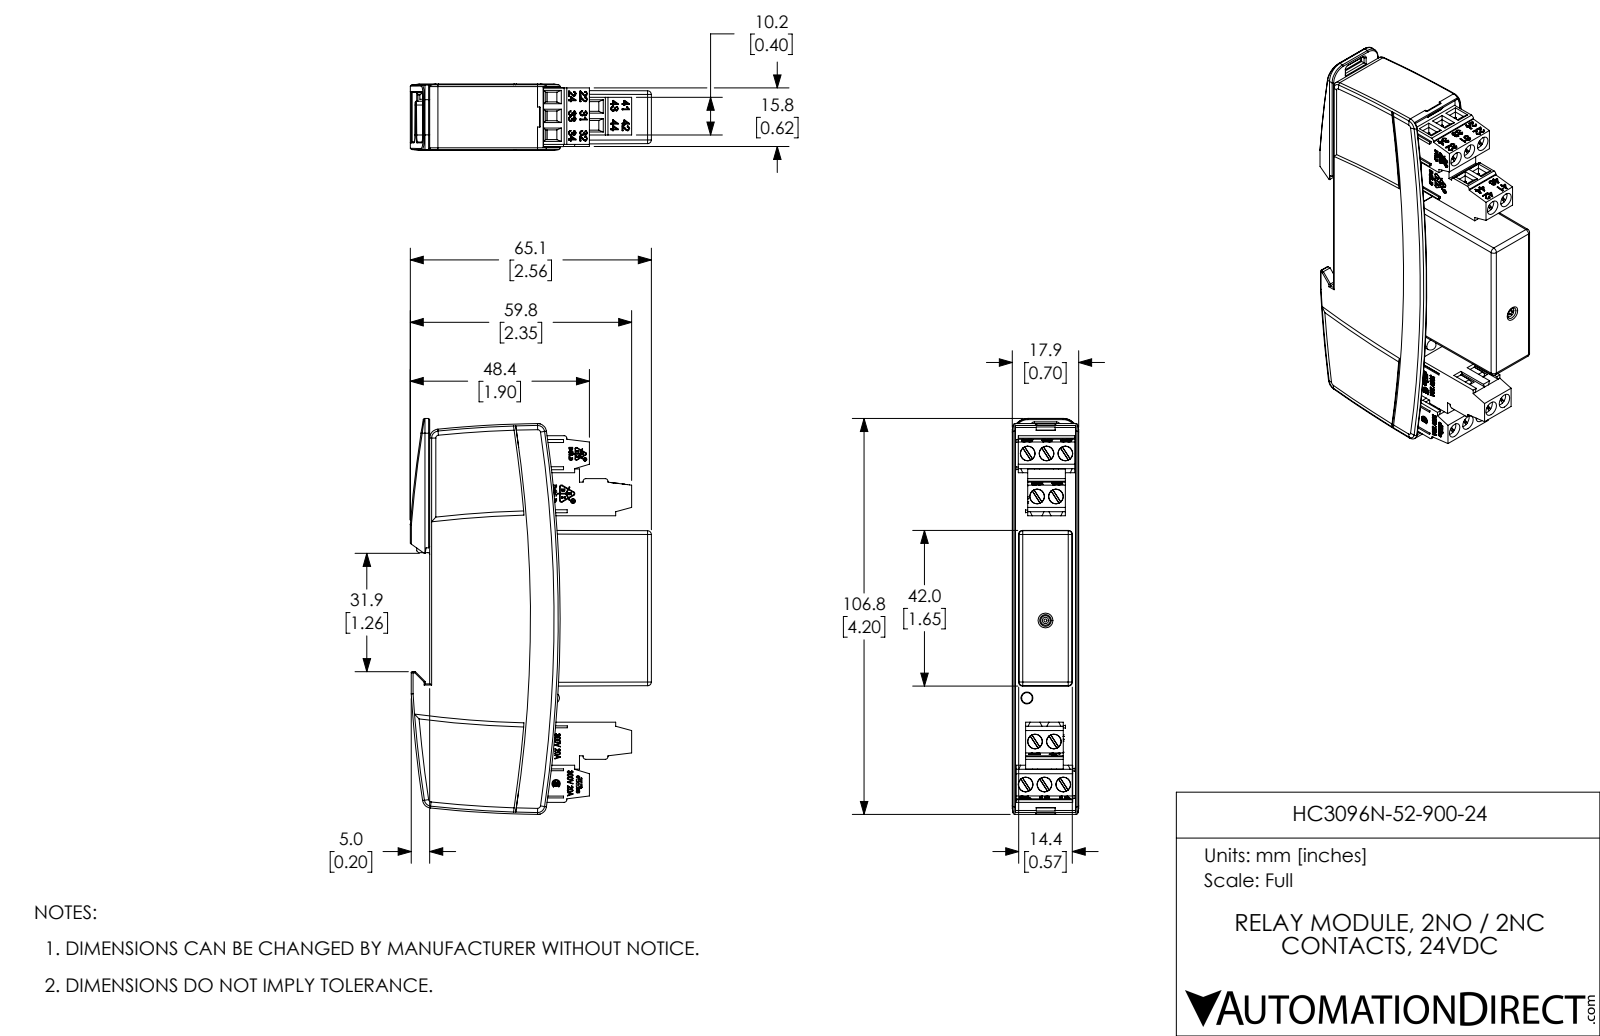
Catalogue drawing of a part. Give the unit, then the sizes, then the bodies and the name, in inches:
Units: inches
Overall size (bounding box): 4.204 × 2.561 × 0.705
Round holes (diameter × count): ⌀0.157 ×10, ⌀0.022 ×4, ⌀0.037 ×2, ⌀0.05 ×2
Round bosses / shafts (diameter × count): ⌀0.154 ×10, ⌀0.019 ×3, ⌀0.046 ×2, ⌀0.034 ×2, ⌀0.126 ×1, ⌀0.114 ×1, ⌀0.031 ×1, ⌀0.019 ×1
Partial cylindrical surfaces — rounded edges, fillets, slot ends (radius × count): R0.006 ×20, R0.012 ×11, R0.02 ×11, R0.005 ×10, R0.039 ×10, R0.004 ×8, R0.006 ×8, R0.031 ×8
Main face-to-face distances: 0.697, 0.705, 0.689, 0.033, 0.663, 0.671, 0.026, 1.177, 1.173, 0.022
Hole centre spacings: 0.467, 0.2, 0.546, 3.059, 3.061, 3.515, 0.253, 0.4
Volume: 5.189 in³ · Surface area: 36.51 in²
Bodies: 1 solid, 3301 faces (2195 planar, 541 cylindrical, 565 other)
Part name (STEP PRODUCT): HC3096N-52-900-24
STEP written by: SolidWorks 2017 (AUTOMOTIVE_DESIGN)
